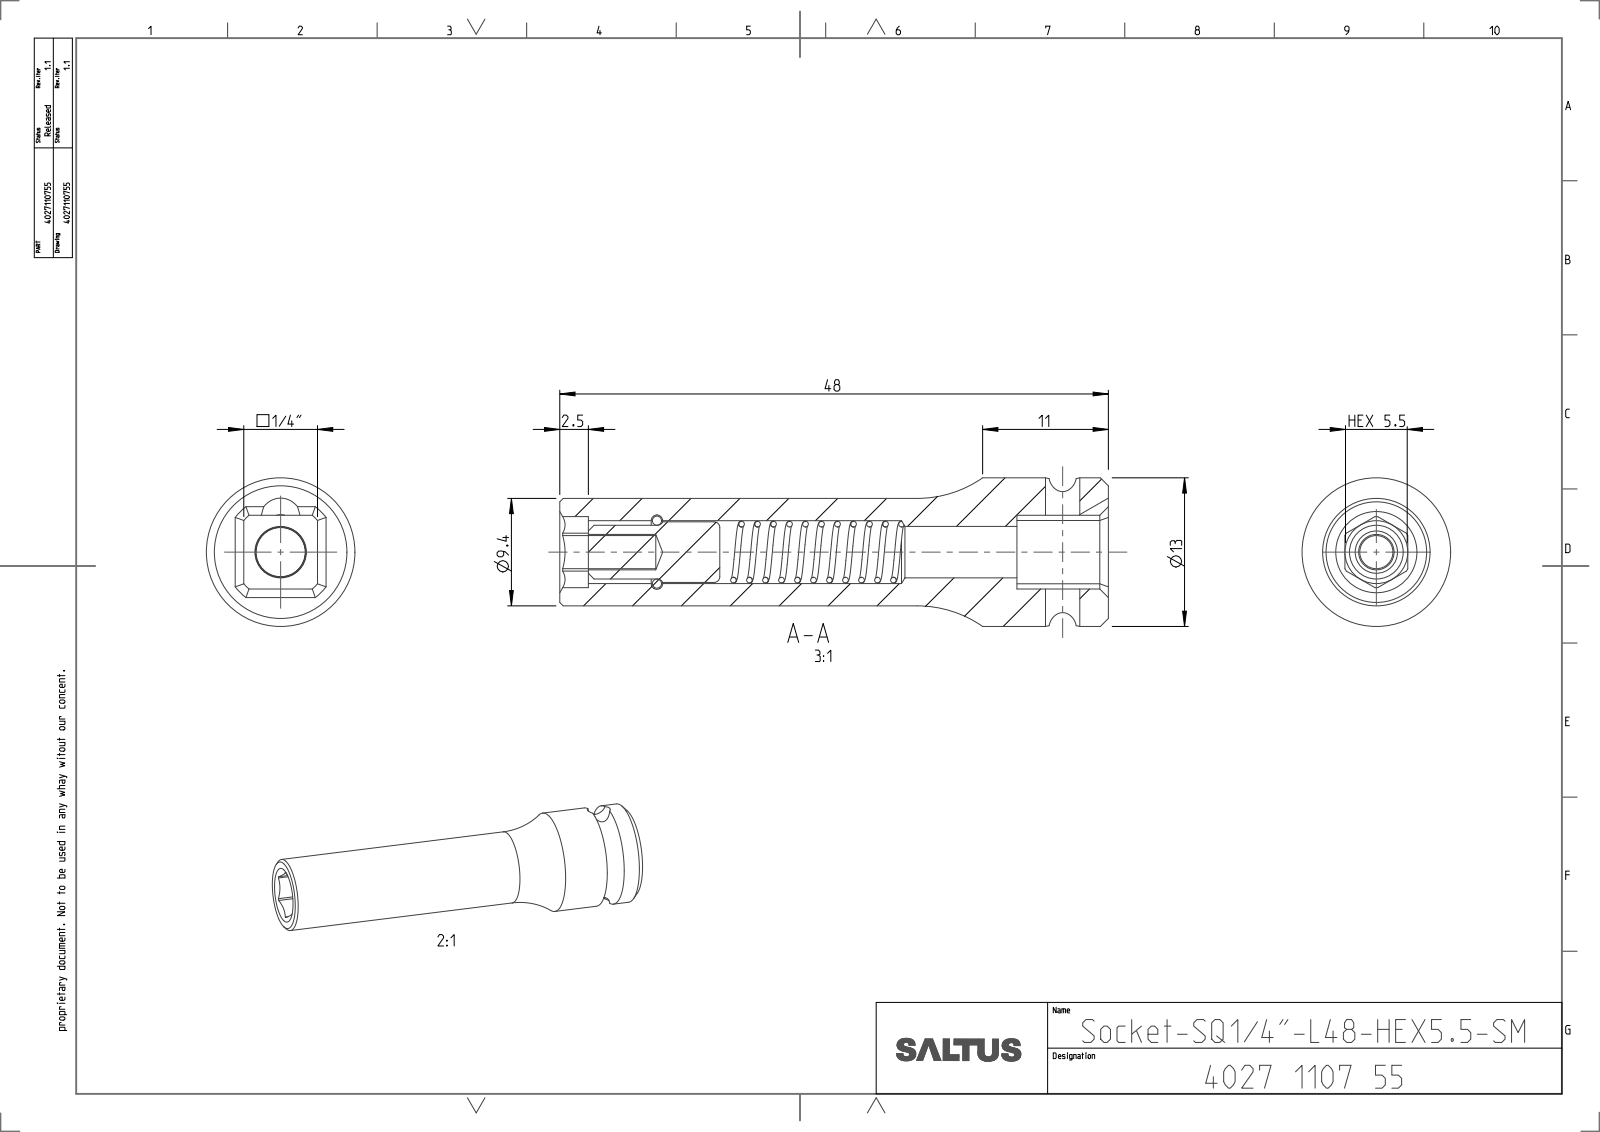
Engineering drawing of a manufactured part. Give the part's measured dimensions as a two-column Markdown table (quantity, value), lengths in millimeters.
| quantity | value |
| --- | --- |
| part name | 4027110755 |
| STEP written by | CREO PARAMETRIC BY PTC INC, 2022414 (CONFIG_CONTROL_DESIGN) |
| units | millimeters |
| bodies | 4 solids, 101 faces (30 planar, 35 cylindrical, 36 other) |
| overall size | 48 × 13 × 13 |
| volume | 3 049 mm³ |
| surface area | 3 272 mm² |
| round holes (diameter × count) | 3 × 1, 3.1 × 1, 4.5 × 1, 5.5 × 1 |
| round bosses / shafts (diameter × count) | 13 × 1, 9.4 × 1, 5.3 × 1, 4.7 × 1, 2.9 × 1 |
| partial cylindrical surfaces (radius × count) | 2 × 1, 3.11 × 1, 4.25 × 1 |
| main face-to-face distances | 6.46, 8, 48, 40, 5.5, 34, 26, 14, 0.48, 5.98 |
